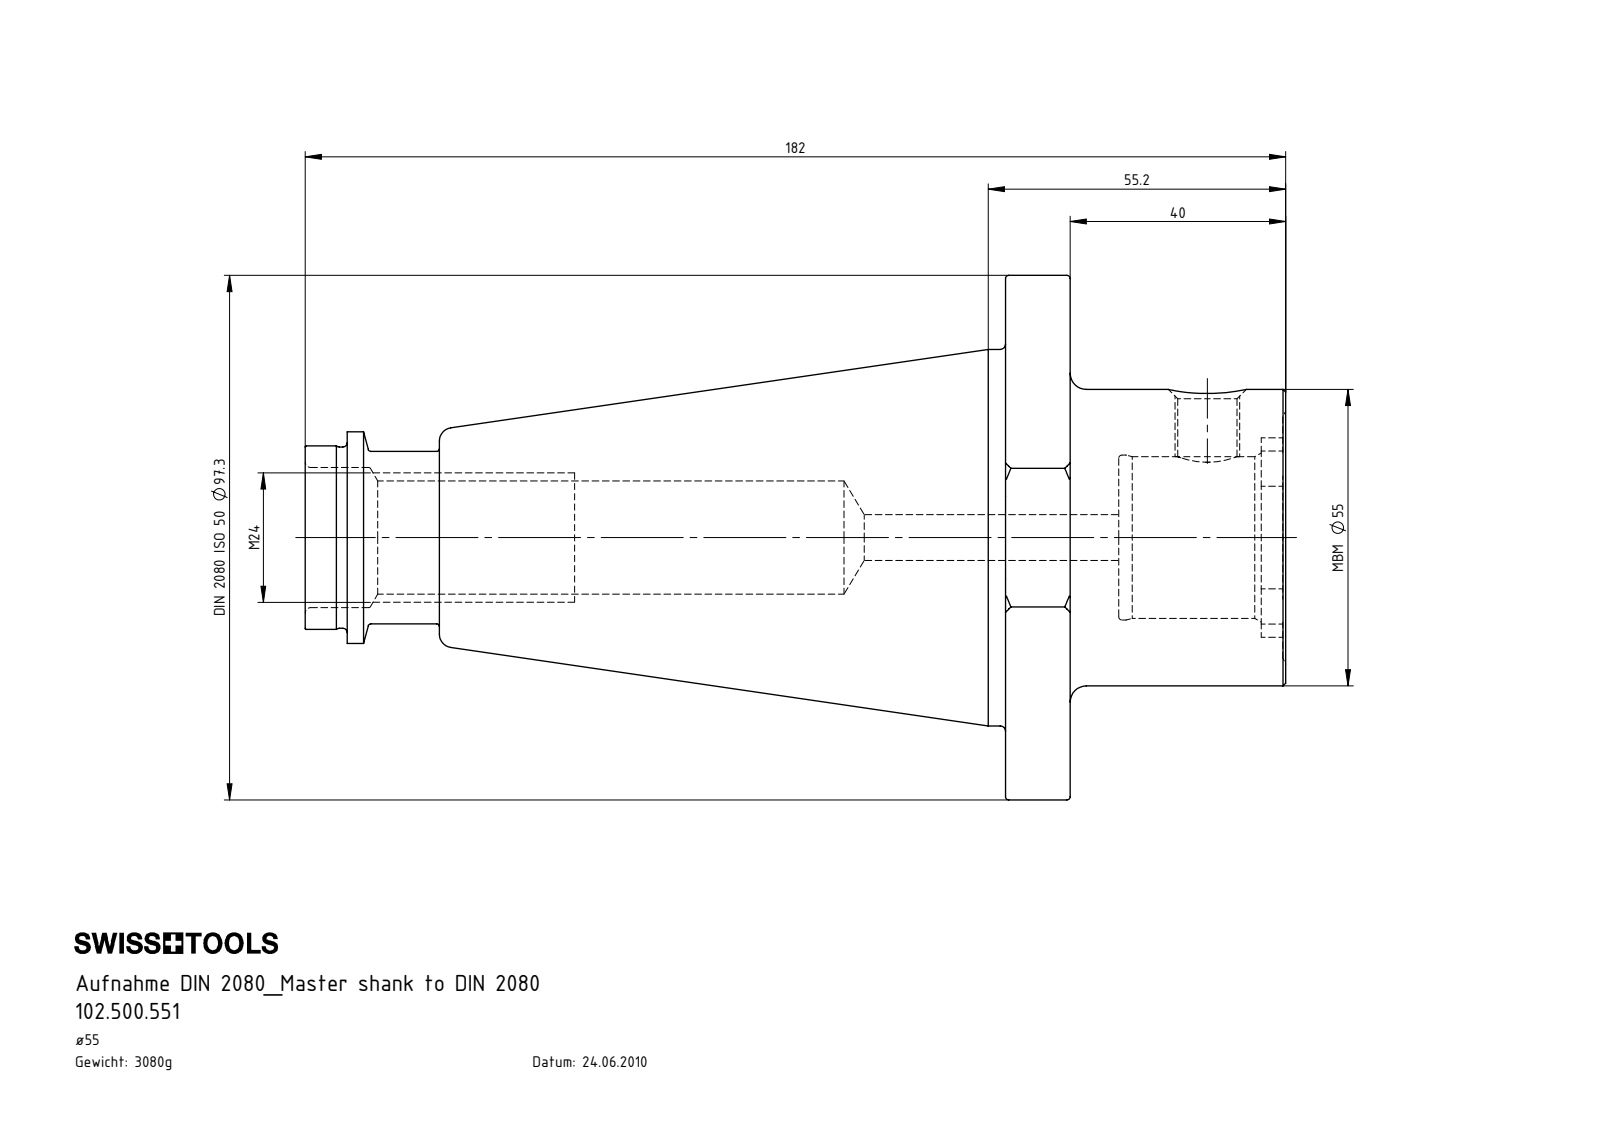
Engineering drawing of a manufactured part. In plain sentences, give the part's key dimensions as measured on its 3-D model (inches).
The part is named "SZ5-MB5.K01.055_B; Kunstoffring SZ5; SZ5-MB5.K01.055; MB5-ER1.001.017_A". Its 3-D file was written by "SolidWorks 2012 (CONFIG_CONTROL_DESIGN)". It is 3 solids with 163 faces: 44 planar, 57 cylindrical and 62 other. Overall it measures 7.165 by 3.831 by 3.694 inches. Its volume is 24.17 cubic inches and its surface area 89.32 square inches. Round holes: 1 of diameter 0.335, 1 of diameter 0.433, 1 of diameter 0.827, 1 of diameter 1.024, 1 of diameter 1.181, 1 of diameter 1.205, 1 of diameter 1.323, 1 of diameter 1.339. Round bosses or shafts: 1 of diameter 3.831, 1 of diameter 2.75, 1 of diameter 2.165, 1 of diameter 1.547, 1 of diameter 1.545, 1 of diameter 1.341, 1 of diameter 1.325, 1 of diameter 1.26. Partial cylindrical surfaces (rounded edges, fillets, slot ends): 12 of radius 0.079, 4 of radius 0.205, 1 of radius 0.728, 1 of radius 0.837. The main face-to-face distances are 0.472, 0.827, 0.354, 2.047, 1.575, 1.22, 1.868, 1.396, 1.041, 0.179.
